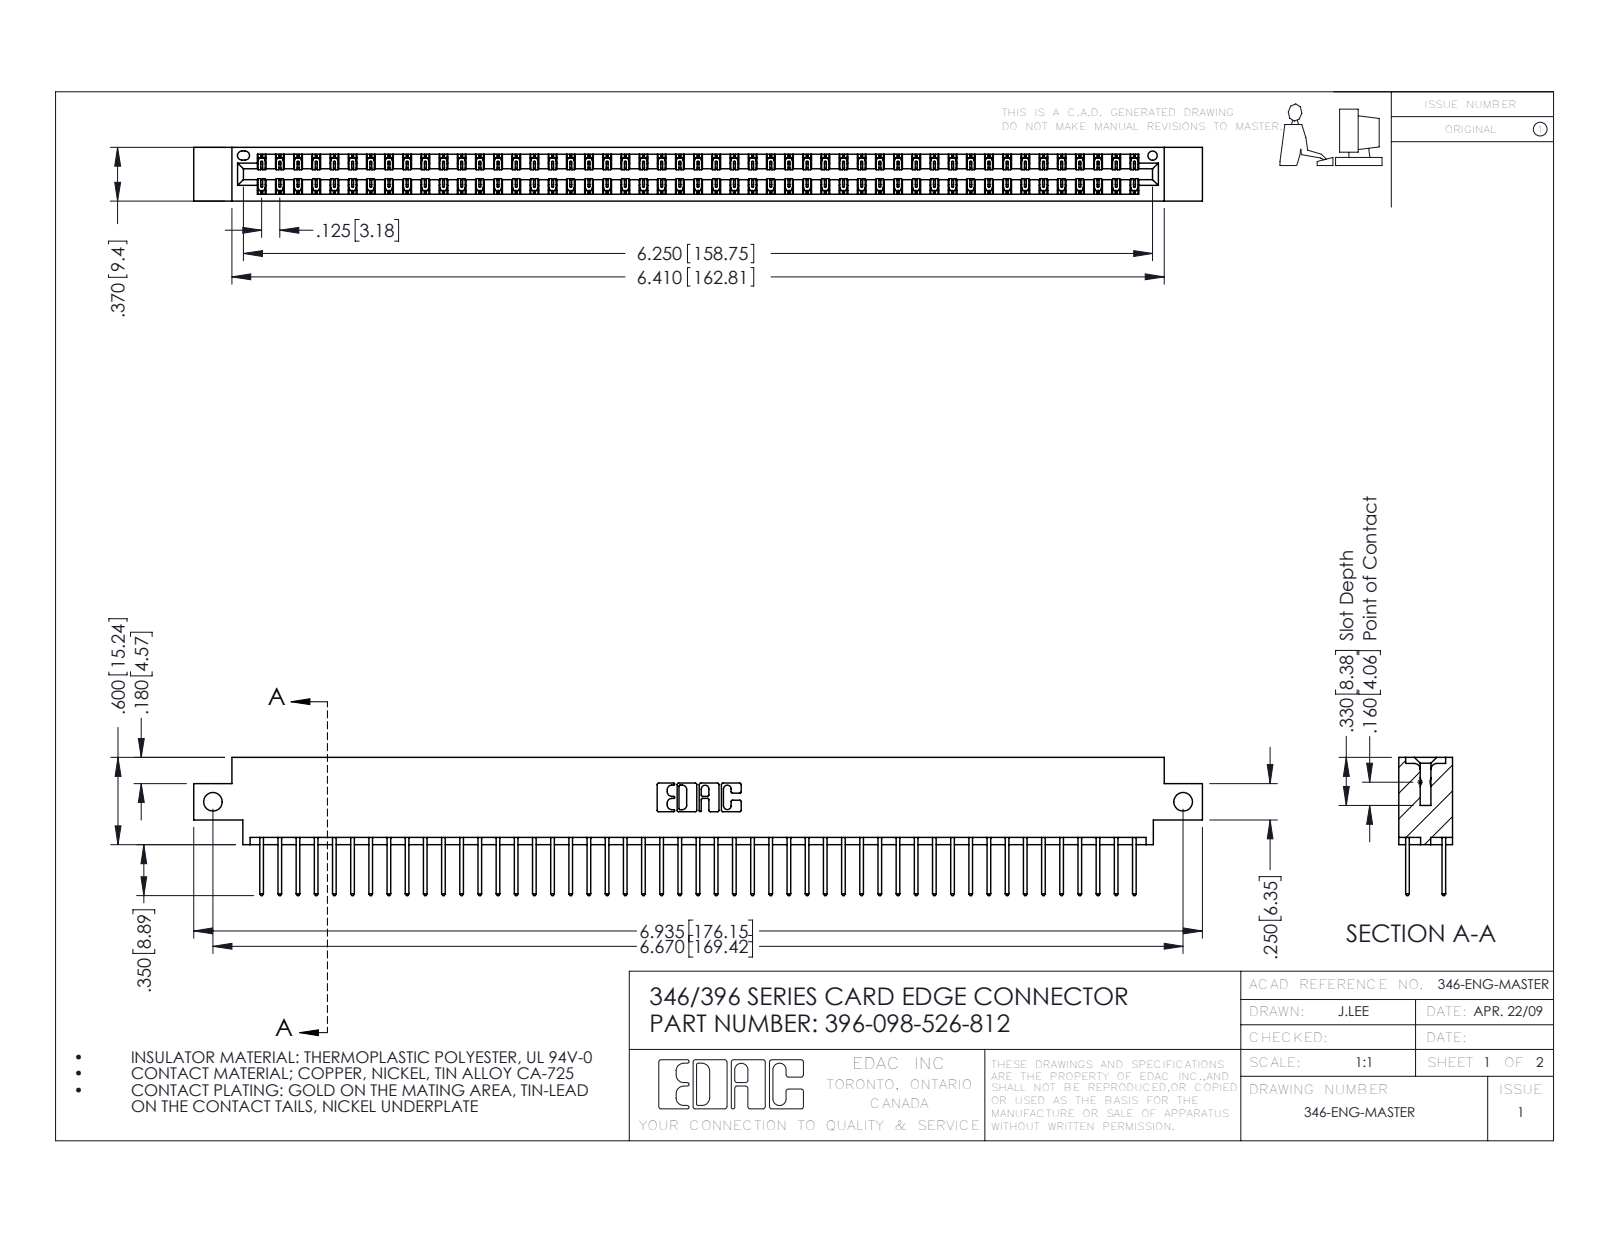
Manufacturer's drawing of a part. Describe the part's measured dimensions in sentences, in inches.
The part is named "396-098-526-812; 346 Part_0.170 Offset - Side Mount; 345-292-001_345-293-126". Its 3-D file was written by "SolidWorks 2016 (CONFIG_CONTROL_DESIGN)". It is 99 solids with 5222 faces: 3510 planar, 1712 cylindrical and 0 other. Overall it measures 6.935 by 0.95 by 0.37 inches. Its volume is 1.047 cubic inches and its surface area 37.89 square inches. Round holes: 2 of diameter 0.128, 1 of diameter 0.064. Partial cylindrical surfaces (rounded edges, fillets, slot ends): 147 of radius 0.006, 98 of radius 0.01, 22 of radius 0.01, 6 of radius 0.007, 6 of radius 0.031, 3 of radius 0.026, 2 of radius 0.014, 2 of radius 0.022. The main face-to-face distances are 0.048, 0.322, 0.25, 0.37, 0.072, 0.298, 0.025, 0.275, 0.148, 0.222. The hole center spacings are 6.67.
